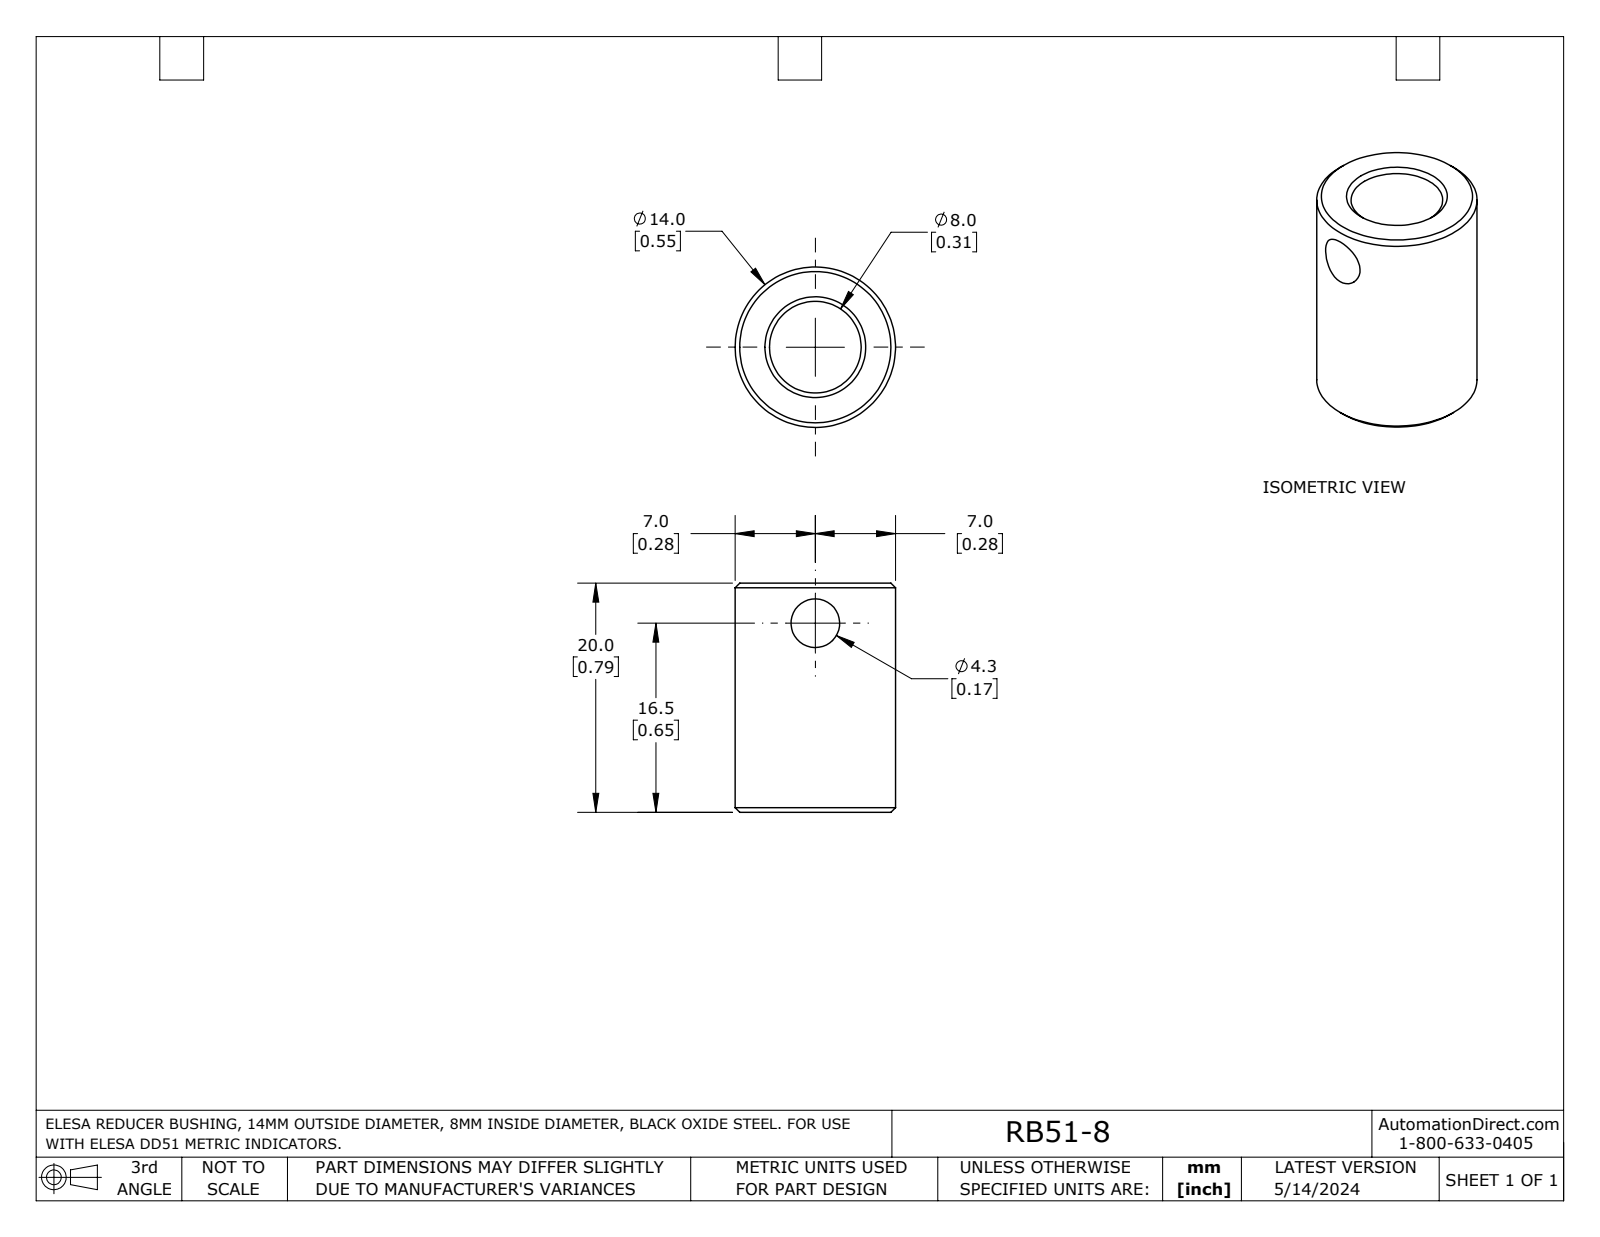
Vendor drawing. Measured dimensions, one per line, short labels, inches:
name: RB51-8
written by: SolidWorks 2023 (AUTOMOTIVE_DESIGN)
unit: in
bodies: 1 solid, 9 faces (2 planar, 3 cylindrical, 4 other)
size: 0.787 × 0.551 × 0.551
volume: 0.123 in³; area: 2.434 in²
holes: 1× ⌀0.167, 1× ⌀0.315
bosses: 1× ⌀0.551
face distances: 0.787
